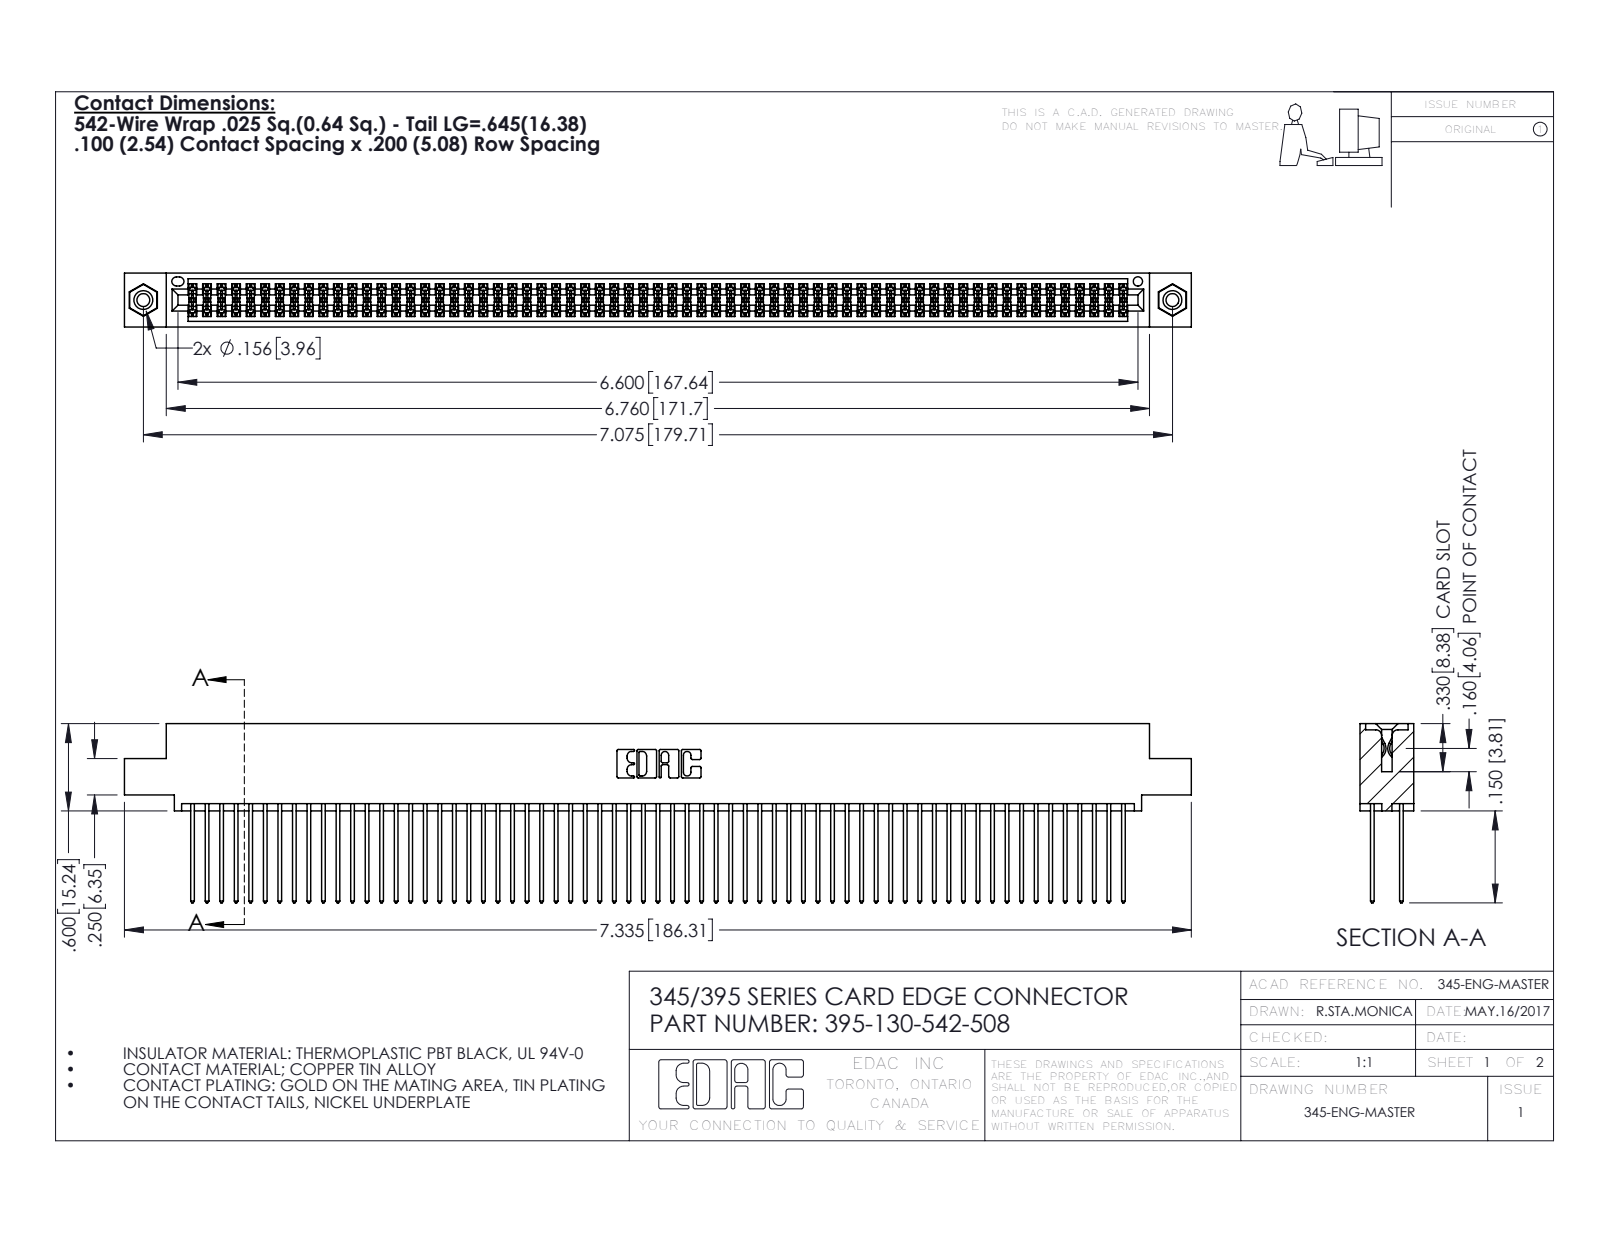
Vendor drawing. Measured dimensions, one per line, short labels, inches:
name: 395-130-542-508; 345 Part_0.110 Offset - 0.156 Dia-TI; 345-292-001_345-293-142; 345-250-001_345-250-003-102
written by: SolidWorks 2016 (CONFIG_CONTROL_DESIGN)
unit: in
bodies: 133 solids, 6690 faces (4406 planar, 2268 cylindrical, 16 other)
size: 7.335 × 1.232 × 0.37
volume: 1.15 in³; area: 48.41 in²
holes: 2× ⌀0.089, 2× ⌀0.125, 2× ⌀0.156, 1× ⌀0.064
bosses: 2× ⌀0.155
rounds: 195× R0.006, 130× R0.01, 22× R0.01, 6× R0.007, 6× R0.031, 3× R0.026, 2× R0.014, 2× R0.019
face distances: 0.072, 0.298, 0.2, 0.098, 0.272, 0.025, 0.225, 0.37, 0.175, 0.149
hole spacings: 0.27, 6.839, 7.075
